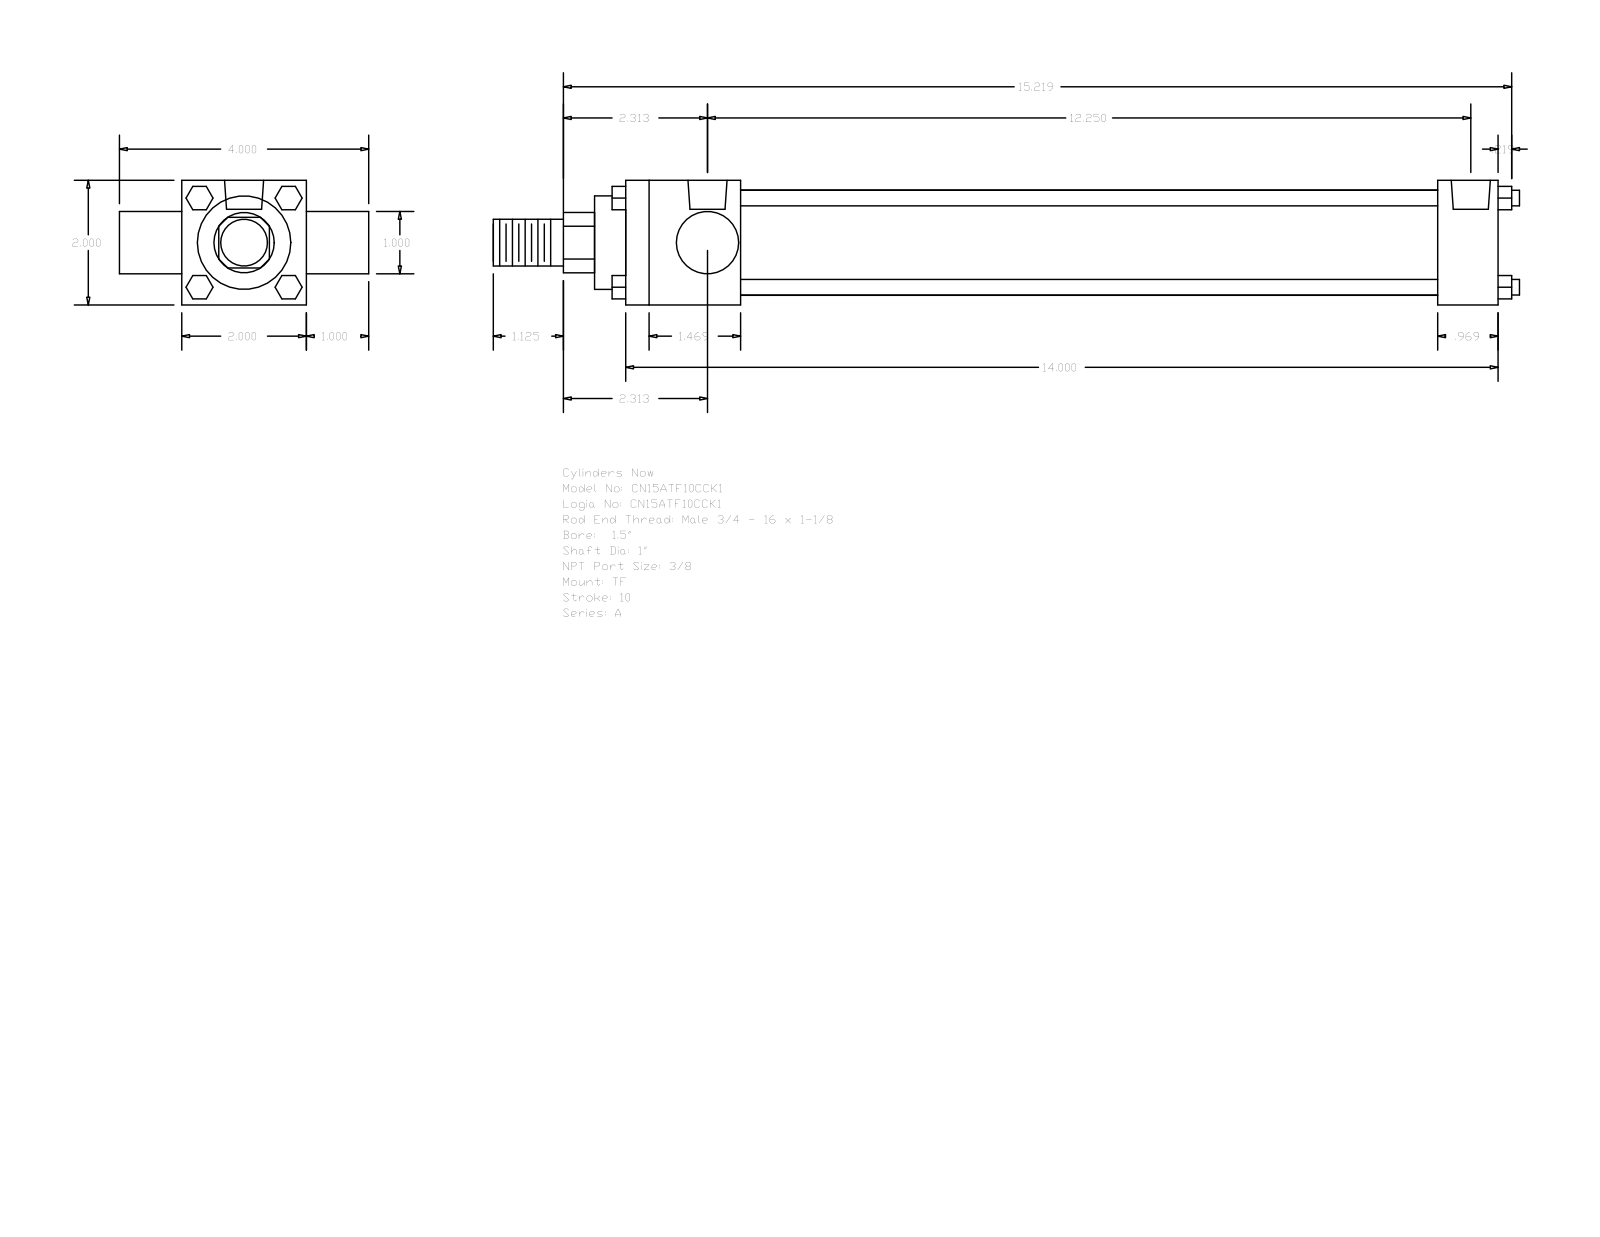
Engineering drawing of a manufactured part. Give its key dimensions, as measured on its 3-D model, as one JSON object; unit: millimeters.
{"part_name": "A_TF__0150_1", "step_written_by": "GSSL Pune (CONFIG_CONTROL_DESIGN)", "units": "millimeters", "bodies": {"solids": 0, "faces": 120, "planar": 92, "cylindrical": 28, "other": 0}, "overall_size": [418.31, 101.6, 50.8], "round_holes": [[5.56, 3], [15.93, 2]], "round_bosses_or_shafts": [[6.35, 4], [25.4, 2], [42.93, 1], [38.1, 1], [19.05, 1]], "partial_cylinders_radius": [[12.29, 1]], "face_to_face_distances": [50.8, 25.4, 355.6, 76.2, 46.83, 330.99, 284.16, 308.77, 24.61, 12.7], "hole_center_spacings": [3.97, 307.18, 303.21, 311.15]}
